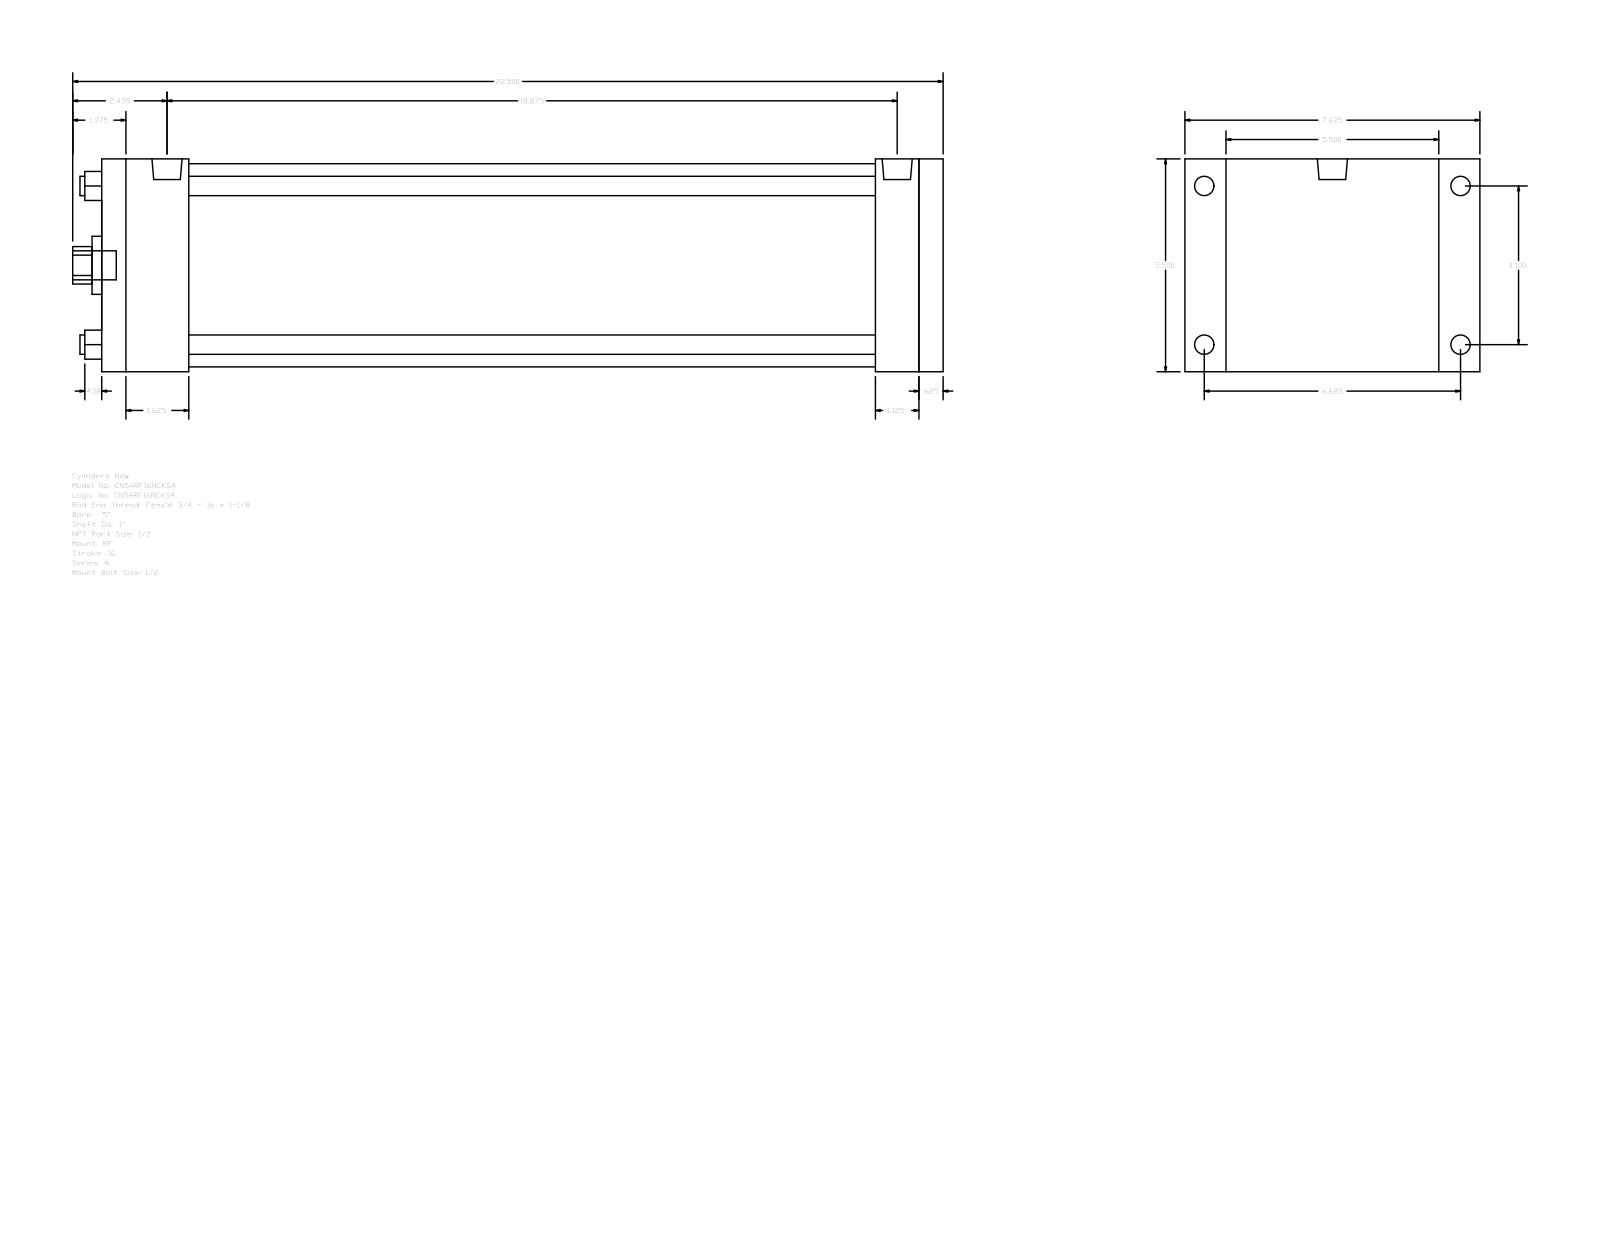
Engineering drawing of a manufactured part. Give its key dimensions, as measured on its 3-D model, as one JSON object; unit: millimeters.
{"part_name": "A_RF__0500_1", "step_written_by": "GSSL Pune (CONFIG_CONTROL_DESIGN)", "units": "millimeters", "bodies": {"solids": 0, "faces": 92, "planar": 64, "cylindrical": 28, "other": 0}, "overall_size": [571.5, 193.68, 139.7], "round_holes": [[12.7, 4], [25.4, 1], [38.1, 1], [133.35, 1]], "round_bosses_or_shafts": [[12.7, 4], [8.73, 4], [19.77, 2], [19.05, 1]], "partial_cylinders_radius": [[12.29, 1]], "face_to_face_distances": [139.7, 552.45, 536.57, 15.88, 28.57, 57.15, 479.42, 495.3, 508, 450.85], "hole_center_spacings": [73.64, 104.14, 147.28]}
